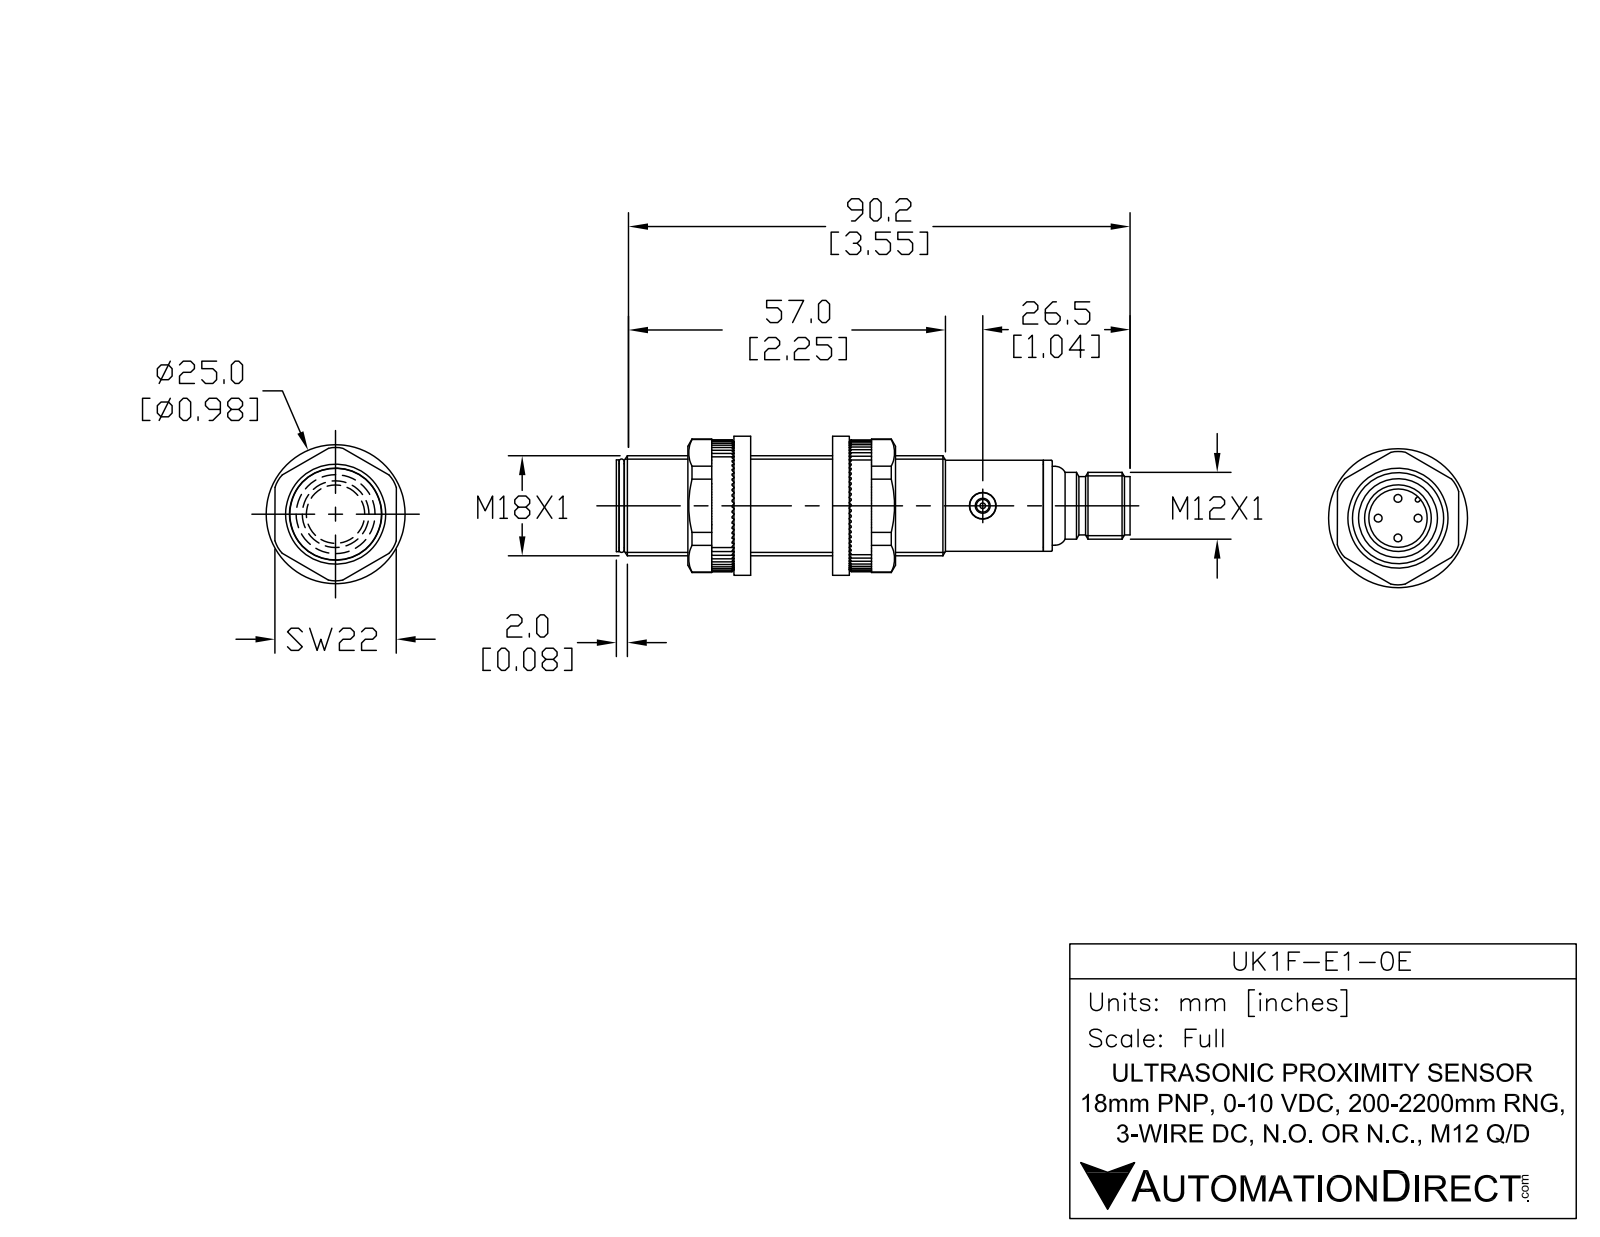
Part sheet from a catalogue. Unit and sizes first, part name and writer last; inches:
Units: inches
Overall size (bounding box): 3.606 × 0.709 × 0.709
Round holes (diameter × count): ⌀0.106 ×1, ⌀0.185 ×1, ⌀0.276 ×1, ⌀0.327 ×1, ⌀0.374 ×1
Round bosses / shafts (diameter × count): ⌀0.039 ×4, ⌀0.709 ×1, ⌀0.654 ×1, ⌀0.646 ×1, ⌀0.622 ×1, ⌀0.559 ×1, ⌀0.472 ×1, ⌀0.413 ×1
Partial cylindrical surfaces — rounded edges, fillets, slot ends (radius × count): R0.024 ×1
Main face-to-face distances: 2.957, 0.039, 2.996, 0.037, 2.994, 0.043, 0.157, 3.055, 3.053, 3.016
Volume: 1.202 in³ · Surface area: 10.68 in²
Bodies: 6 solids, 106 faces (21 planar, 48 cylindrical, 37 other)
Part name (STEP PRODUCT): UK1F-E1-0E
STEP written by: SolidWorks 2017 (AUTOMOTIVE_DESIGN)
